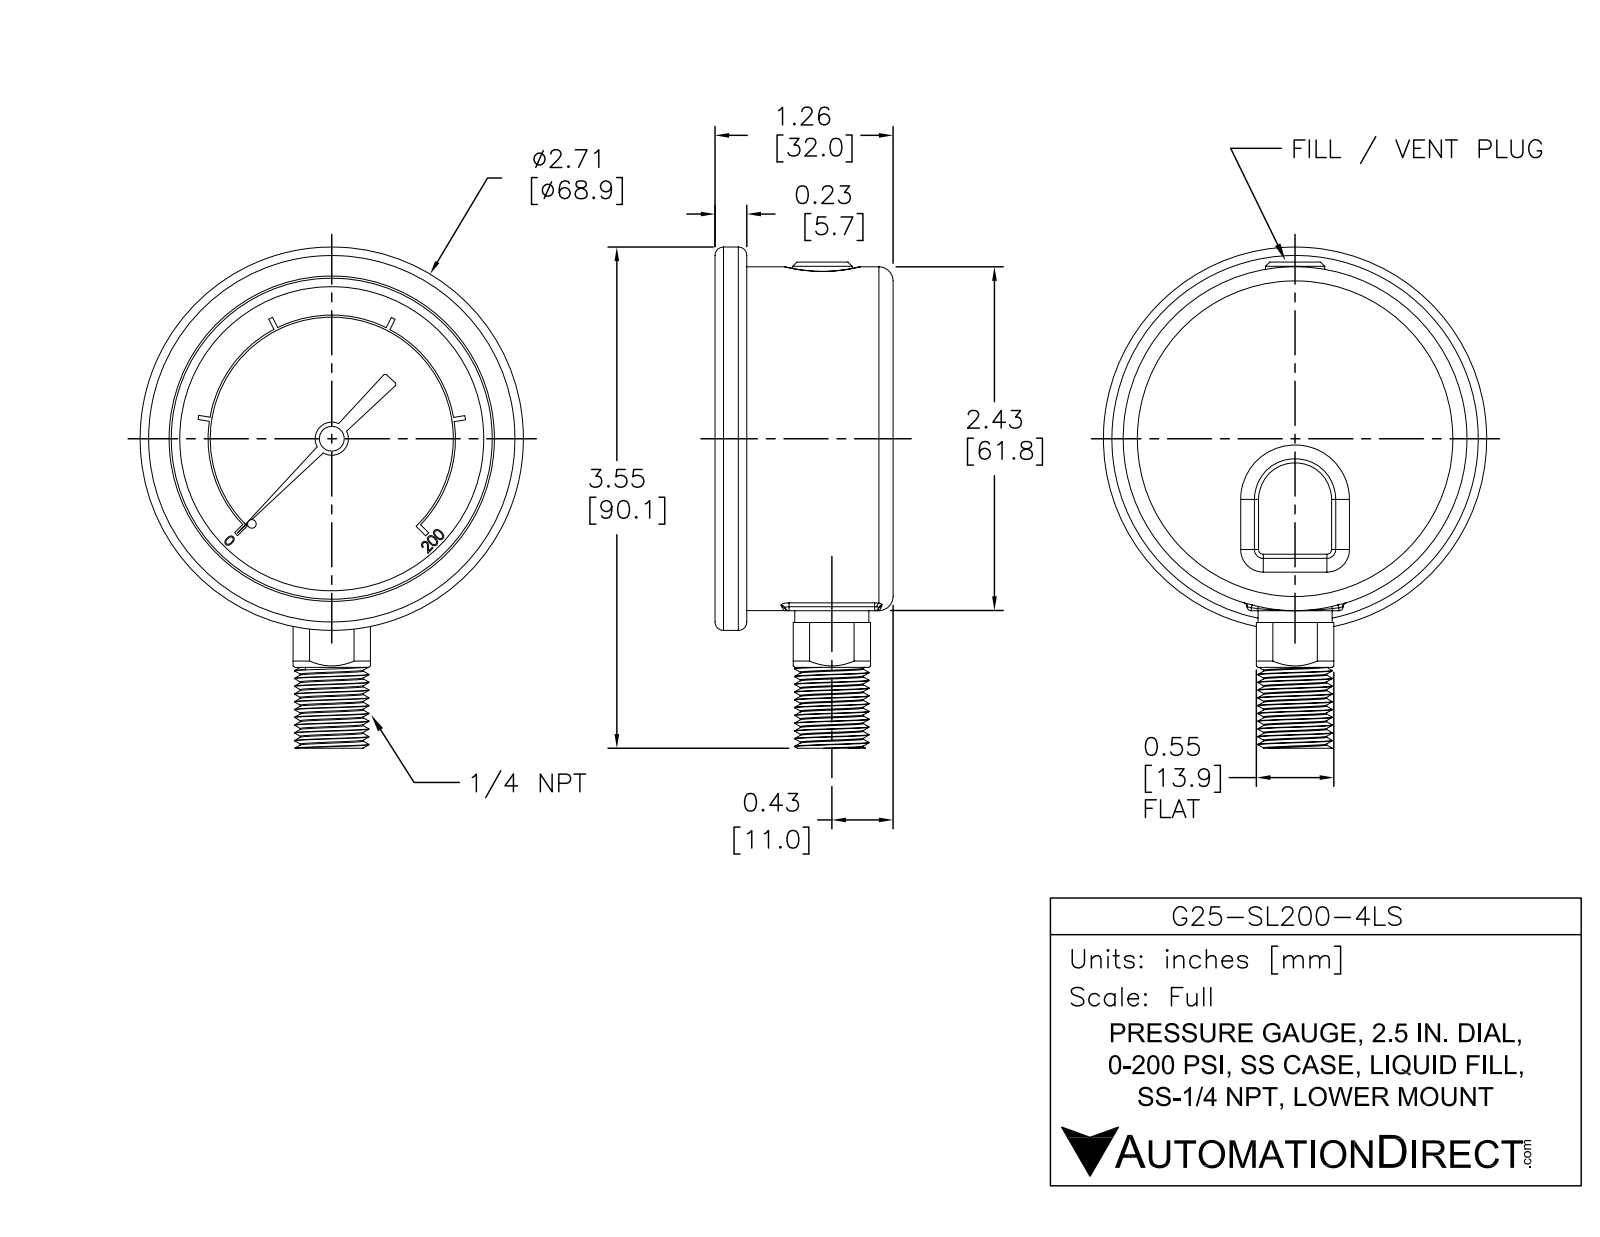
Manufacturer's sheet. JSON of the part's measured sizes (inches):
{"part_name": "G25-SL200-4LS", "step_written_by": "SolidWorks 2021 (AUTOMOTIVE_DESIGN)", "units": "inches", "bodies": {"solids": 1, "faces": 349, "planar": 195, "cylindrical": 85, "other": 69}, "overall_size": [3.546, 2.713, 1.26], "volume_in3": 5.273, "surface_area_in2": 24.68, "round_holes": [[0.027, 1], [0.071, 1], [0.119, 1], [2.272, 1]], "round_bosses_or_shafts": [[2.713, 1], [2.433, 1], [0.524, 1], [0.42, 1], [0.235, 1], [0.176, 1], [0.14, 1], [0.041, 1]], "partial_cylinders_radius": [[0.03, 9], [0.1, 3], [0.015, 2], [0.316, 1], [0.86, 1], [0.875, 1]], "face_to_face_distances": [1.01, 1.26, 0.25, 1.035, 0.025, 0.225, 0.1, 0.91, 0.935, 1.16], "hole_center_spacings": [0.067]}
